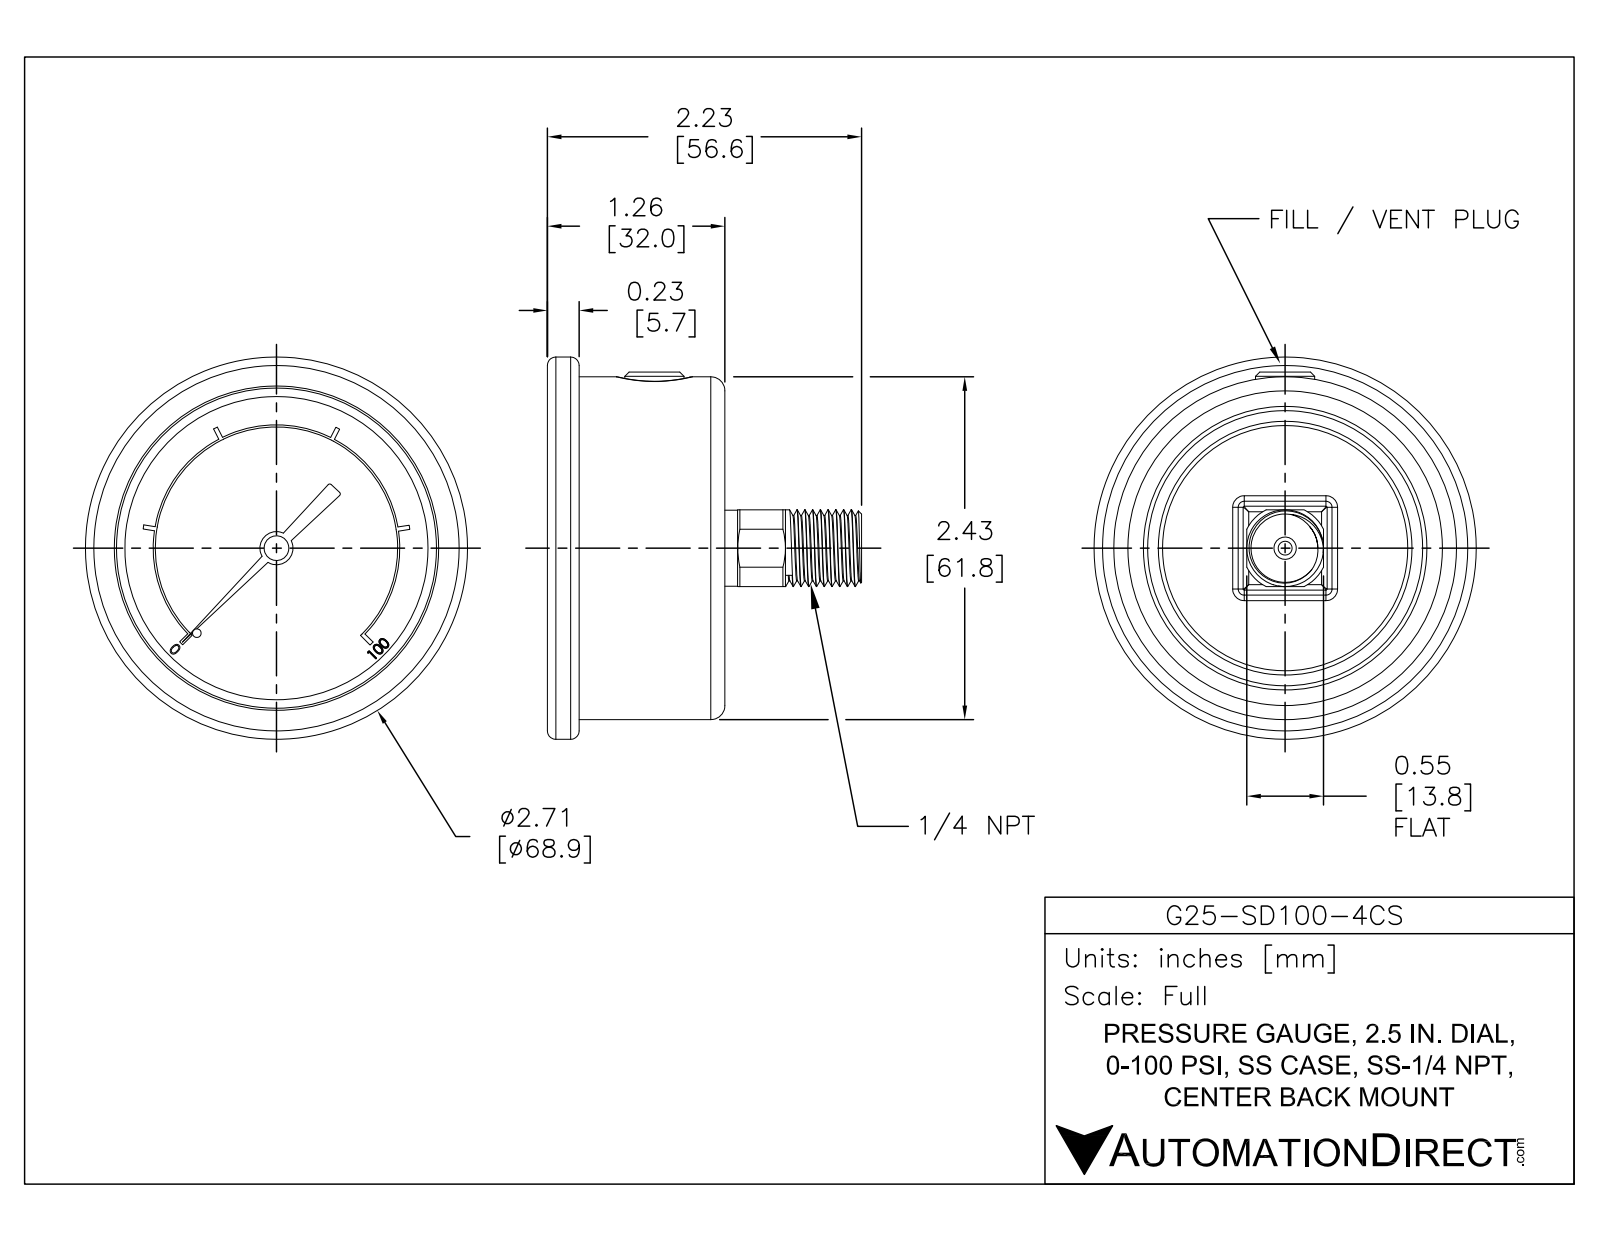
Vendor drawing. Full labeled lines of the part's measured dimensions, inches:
Part name (STEP PRODUCT): G25-SD100-4CS
STEP written by: SolidWorks 2021 (AUTOMOTIVE_DESIGN)
Units: inches
Bodies: 1 solid, 348 faces (208 planar, 83 cylindrical, 57 other)
Overall size (bounding box): 2.713 × 2.713 × 2.23
Volume: 5.168 in³ · Surface area: 24.82 in²
Round holes (diameter × count): ⌀0.071 ×1, ⌀0.098 ×1, ⌀2.272 ×1
Round bosses / shafts (diameter × count): ⌀2.713 ×1, ⌀2.433 ×1, ⌀0.545 ×1, ⌀0.54 ×1, ⌀0.42 ×1, ⌀0.235 ×1, ⌀0.176 ×1, ⌀0.14 ×1
Partial cylindrical surfaces — rounded edges, fillets, slot ends (radius × count): R0.06 ×8, R0.015 ×2, R0.304 ×1, R0.86 ×1, R0.875 ×1
Main face-to-face distances: 0.95, 1.2, 0.25, 0.06, 1.01, 1.26, 1.035, 0.975, 0.025, 0.225
